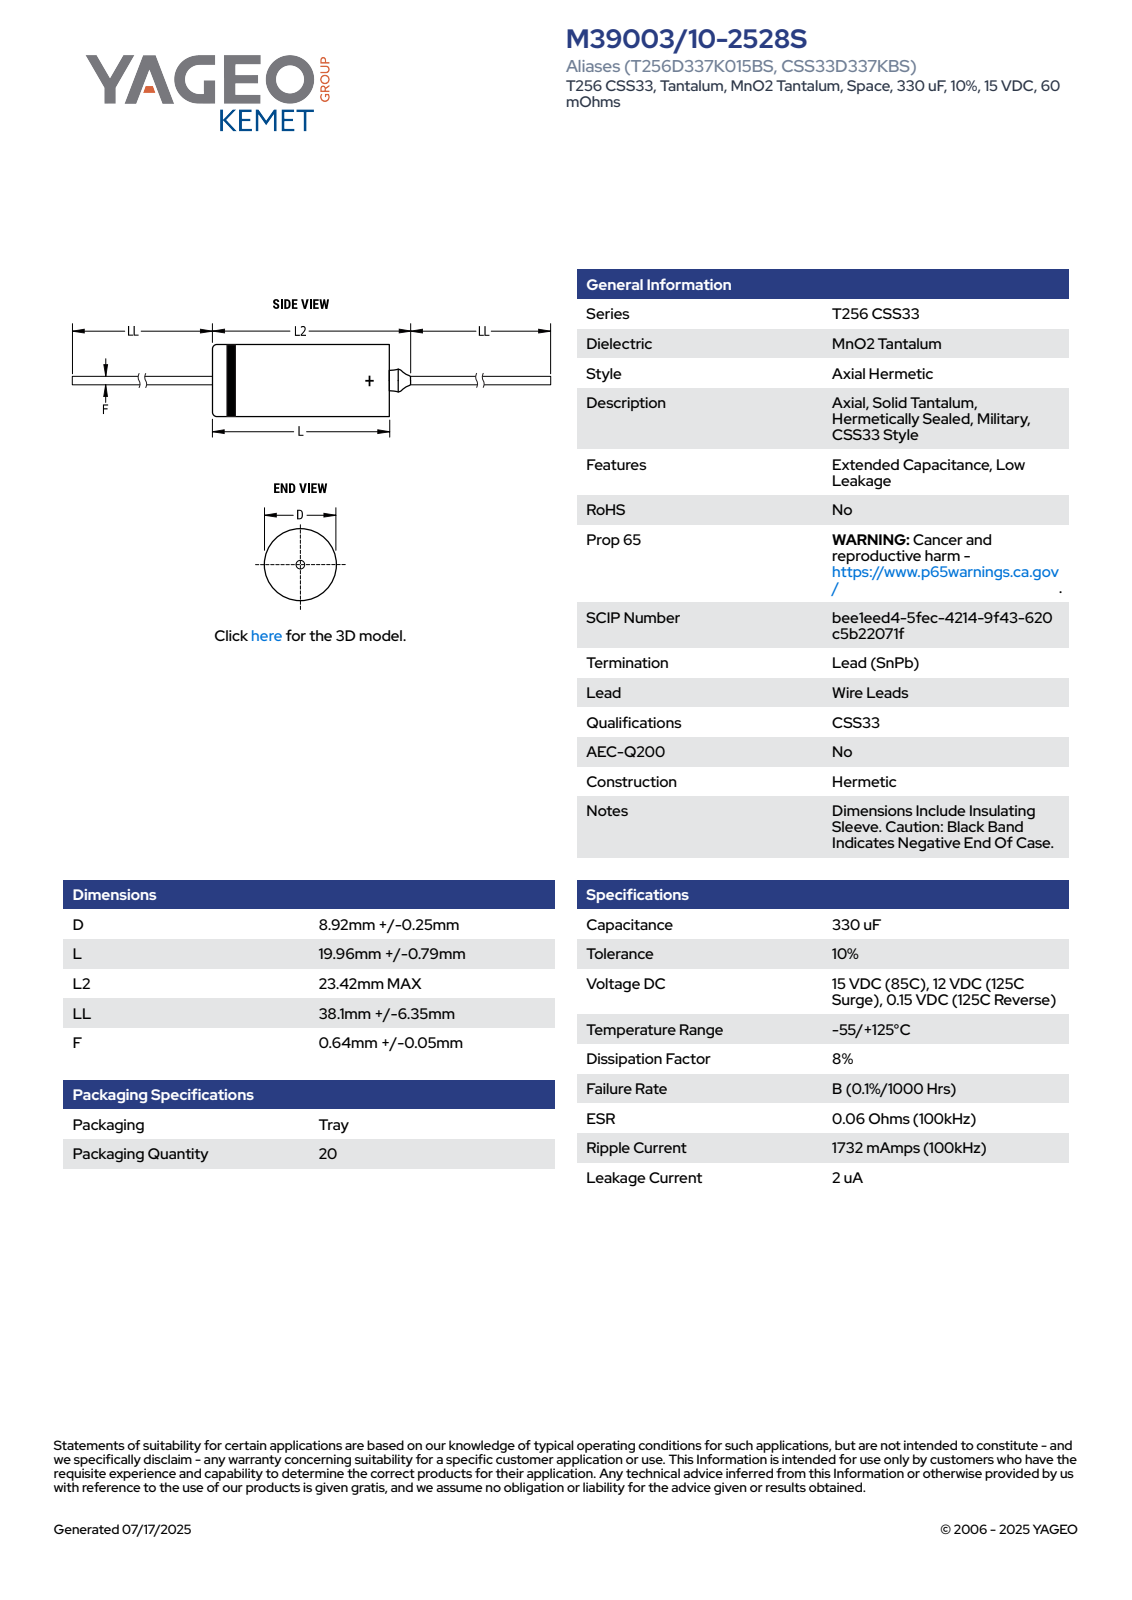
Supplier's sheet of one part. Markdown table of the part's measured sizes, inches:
| quantity | value |
| --- | --- |
| part name | CTAM_D9.17L20.75L223.42LL44.45F0.69 |
| STEP written by | SolidWorks 2014 (AUTOMOTIVE_DESIGN) |
| units | inches |
| bodies | 1 solid, 98 faces (29 planar, 30 cylindrical, 39 other) |
| overall size | 4.317 × 0.361 × 0.361 |
| volume | 0.067 in³ |
| surface area | 1.676 in² |
| round holes (diameter × count) | 0.345 × 1 |
| round bosses / shafts (diameter × count) | 0.361 × 1, 0.052 × 1, 0.051 × 1, 0.027 × 1 |
| partial cylindrical surfaces (radius × count) | 0.18 × 1 |
| main face-to-face distances | 0.607, 0.81, 0.203, 1.757, 2.364, 2.567, 4.317, 2.56, 1.953, 1.75 |
